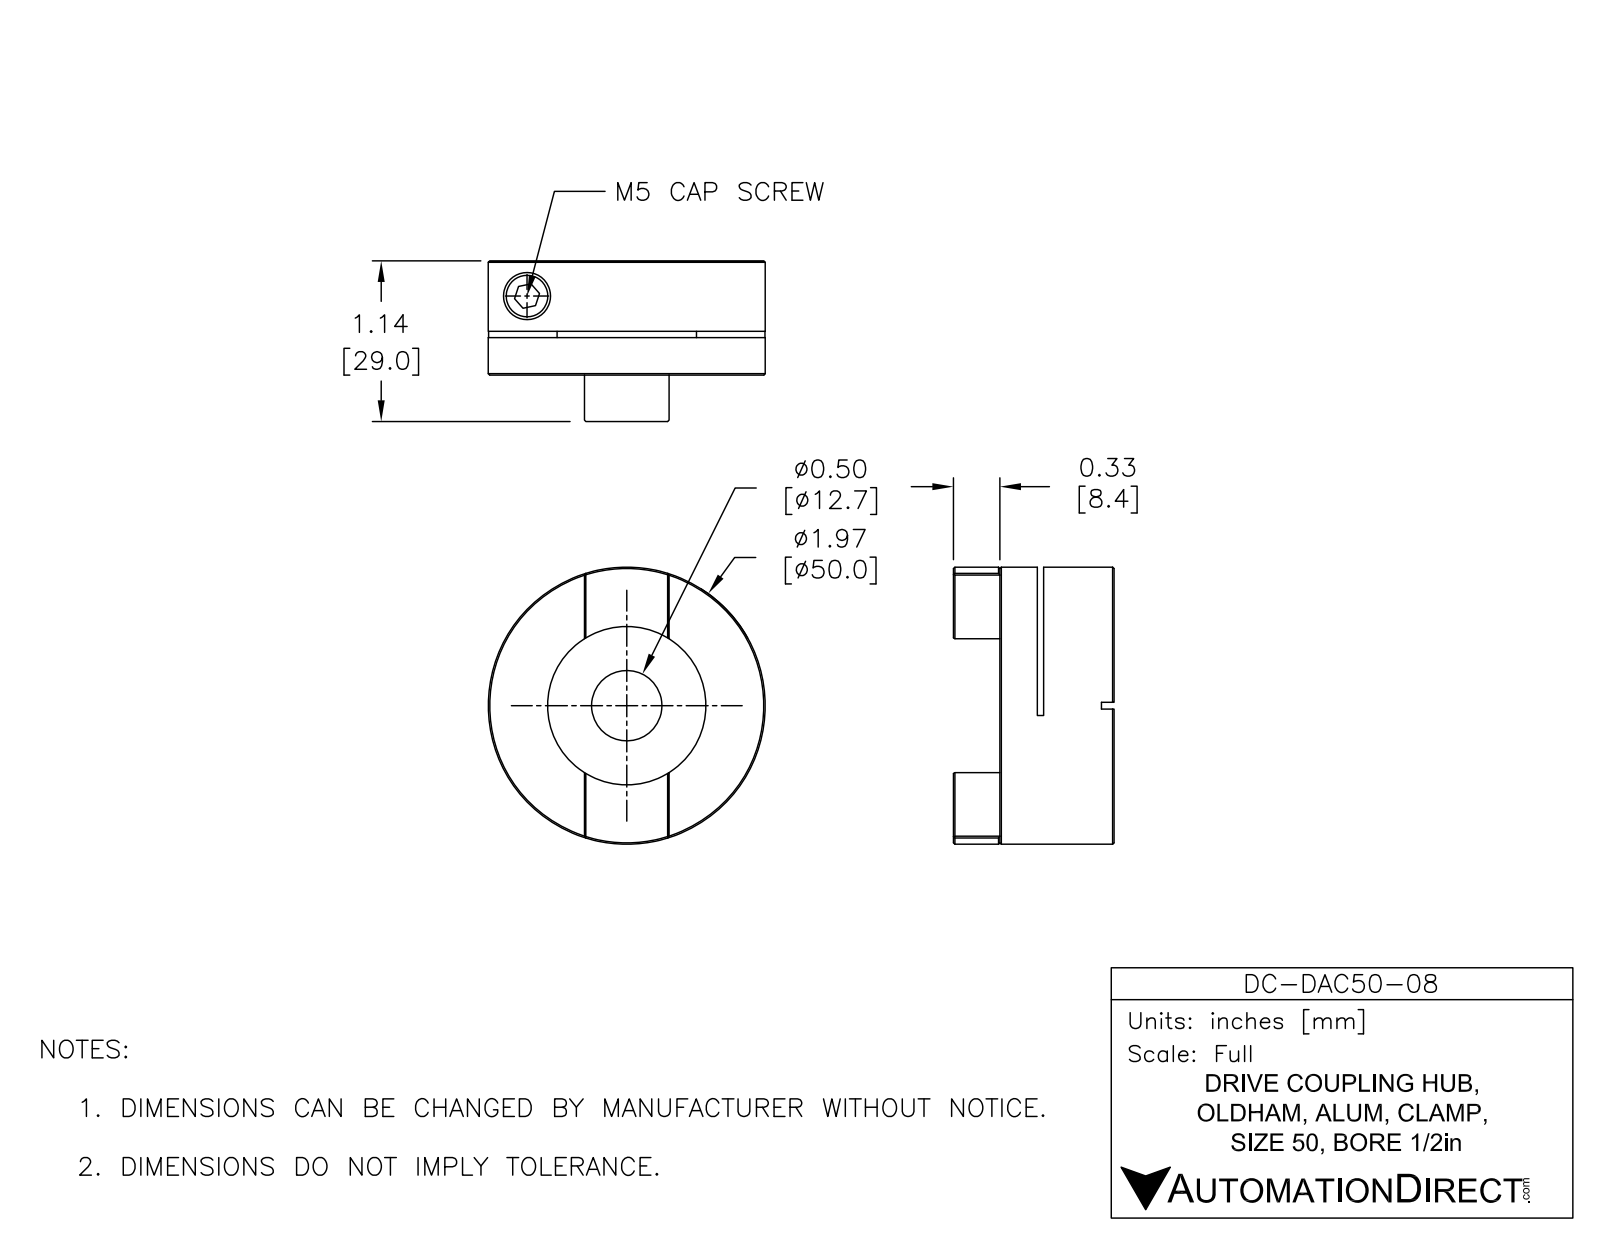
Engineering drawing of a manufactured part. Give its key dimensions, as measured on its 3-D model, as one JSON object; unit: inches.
{"part_name": "DC-DAC50-08", "step_written_by": "SolidWorks 2015 (AUTOMOTIVE_DESIGN)", "units": "inches", "bodies": {"solids": 1, "faces": 57, "planar": 30, "cylindrical": 19, "other": 8}, "overall_size": [1.969, 1.969, 1.141], "volume_in3": 2.229, "surface_area_in2": 18.52, "round_holes": [[0.217, 1], [0.394, 1], [0.5, 1], [1.125, 1]], "round_bosses_or_shafts": [[1.969, 1], [1.948, 1]], "partial_cylinders_radius": [[1, 1]], "face_to_face_distances": [0.545, 0.5, 0.045, 0.811, 0.311, 0.266, 0.741, 0.241, 0.196, 0.07]}
